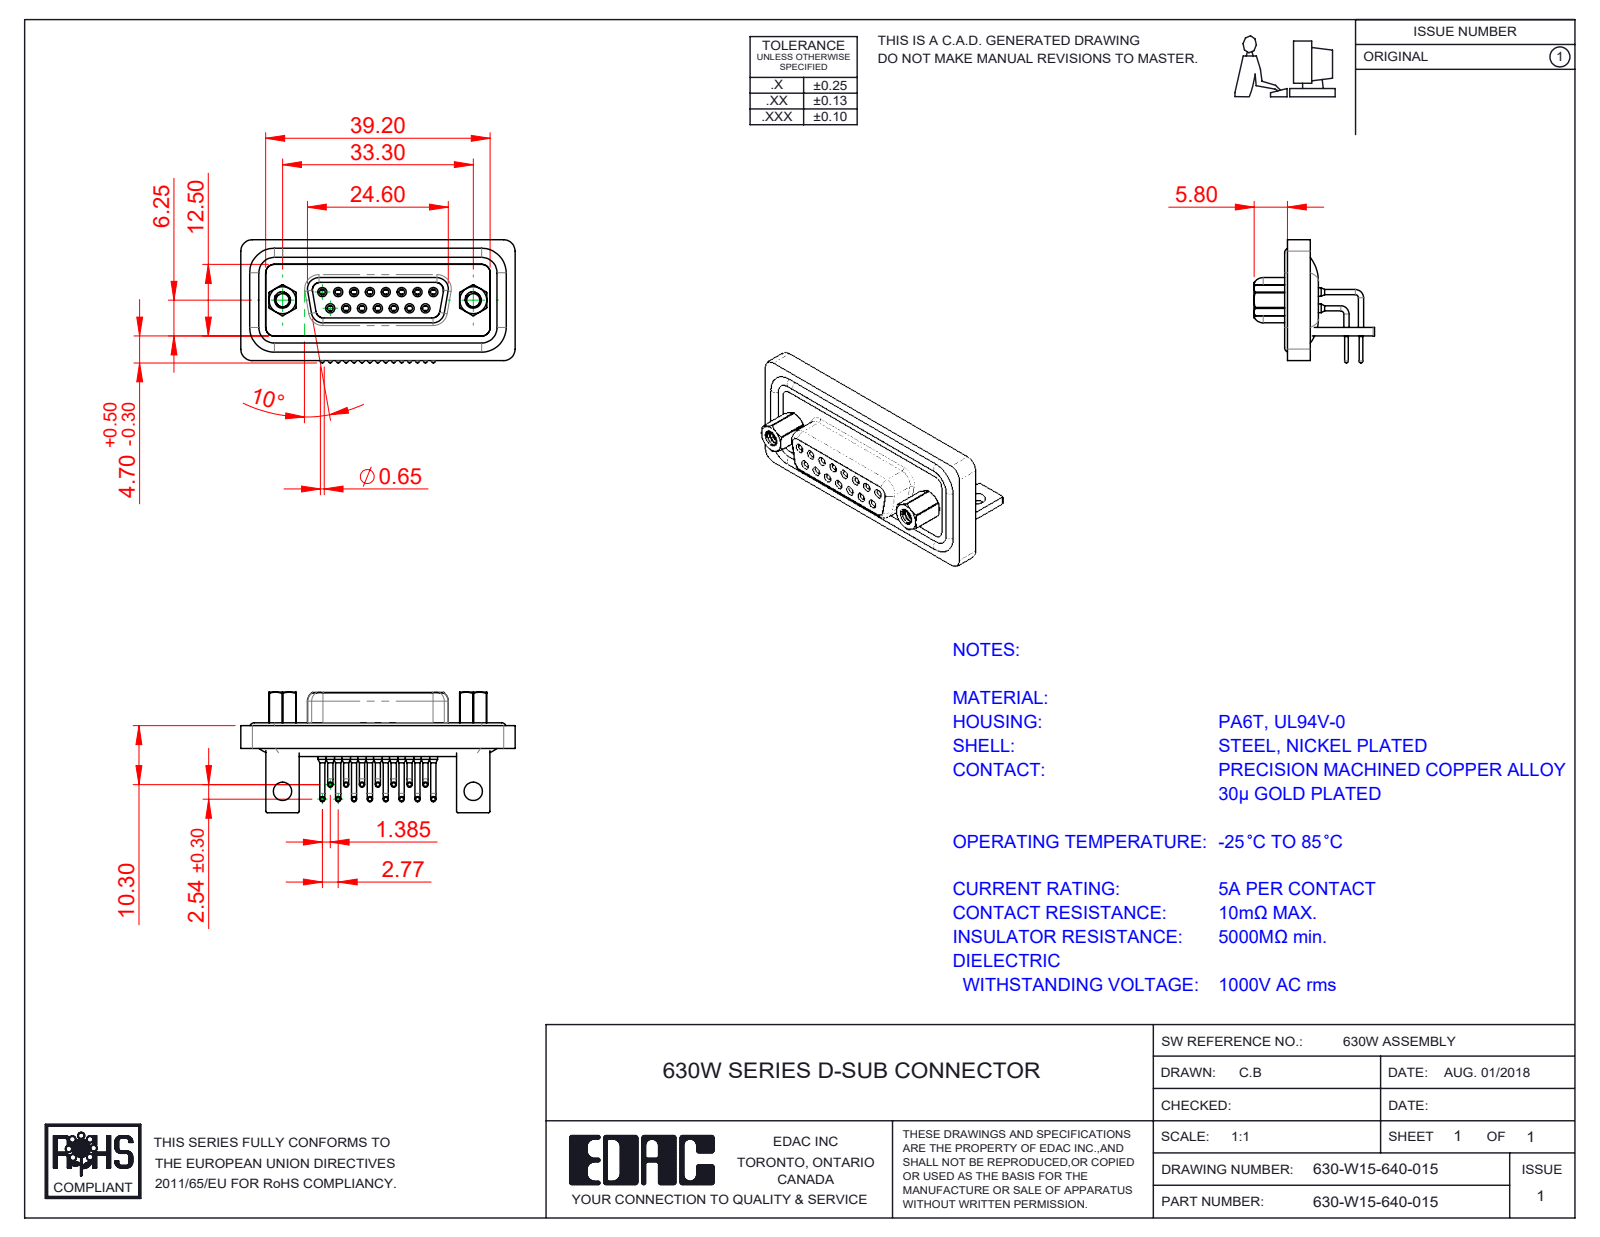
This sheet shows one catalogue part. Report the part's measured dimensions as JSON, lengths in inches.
{"part_name": "630-W15-640-015; 630W 4-40 Threaded Rivet_Stabilizer; 630W Stabilizer Bracket; 630W Contact Row 1 (+5 more)", "step_written_by": "SolidWorks 2016 (CONFIG_CONTROL_DESIGN)", "units": "inches", "bodies": {"solids": 25, "faces": 1294, "planar": 348, "cylindrical": 615, "other": 331}, "overall_size": [1.885, 0.846, 0.829], "volume_in3": 0.359, "surface_area_in2": 16.06, "round_holes": [[0.039, 15], [0.043, 15], [0.059, 15], [0.067, 15], [0.071, 15], [0.079, 15], [0.089, 2], [0.09, 2], [0.126, 2], [0.157, 2], [0.189, 2], [0.193, 2]], "round_bosses_or_shafts": [[0.035, 30], [0.063, 19], [0.059, 15], [0.026, 15], [0.11, 2], [0.197, 1]], "partial_cylinders_radius": [[0.079, 17], [0.059, 14], [0.01, 12], [0.053, 8], [0.106, 6], [0.02, 5], [0.035, 4], [0.063, 4]], "face_to_face_distances": [0.016, 0.071, 0.063, 0.043, 0.098, 0.114, 0.169, 0.386, 0.228, 0.02], "hole_center_spacings": [0.124, 0.109, 0.218, 0.327, 0.125, 0.124, 0.436, 0.198]}
